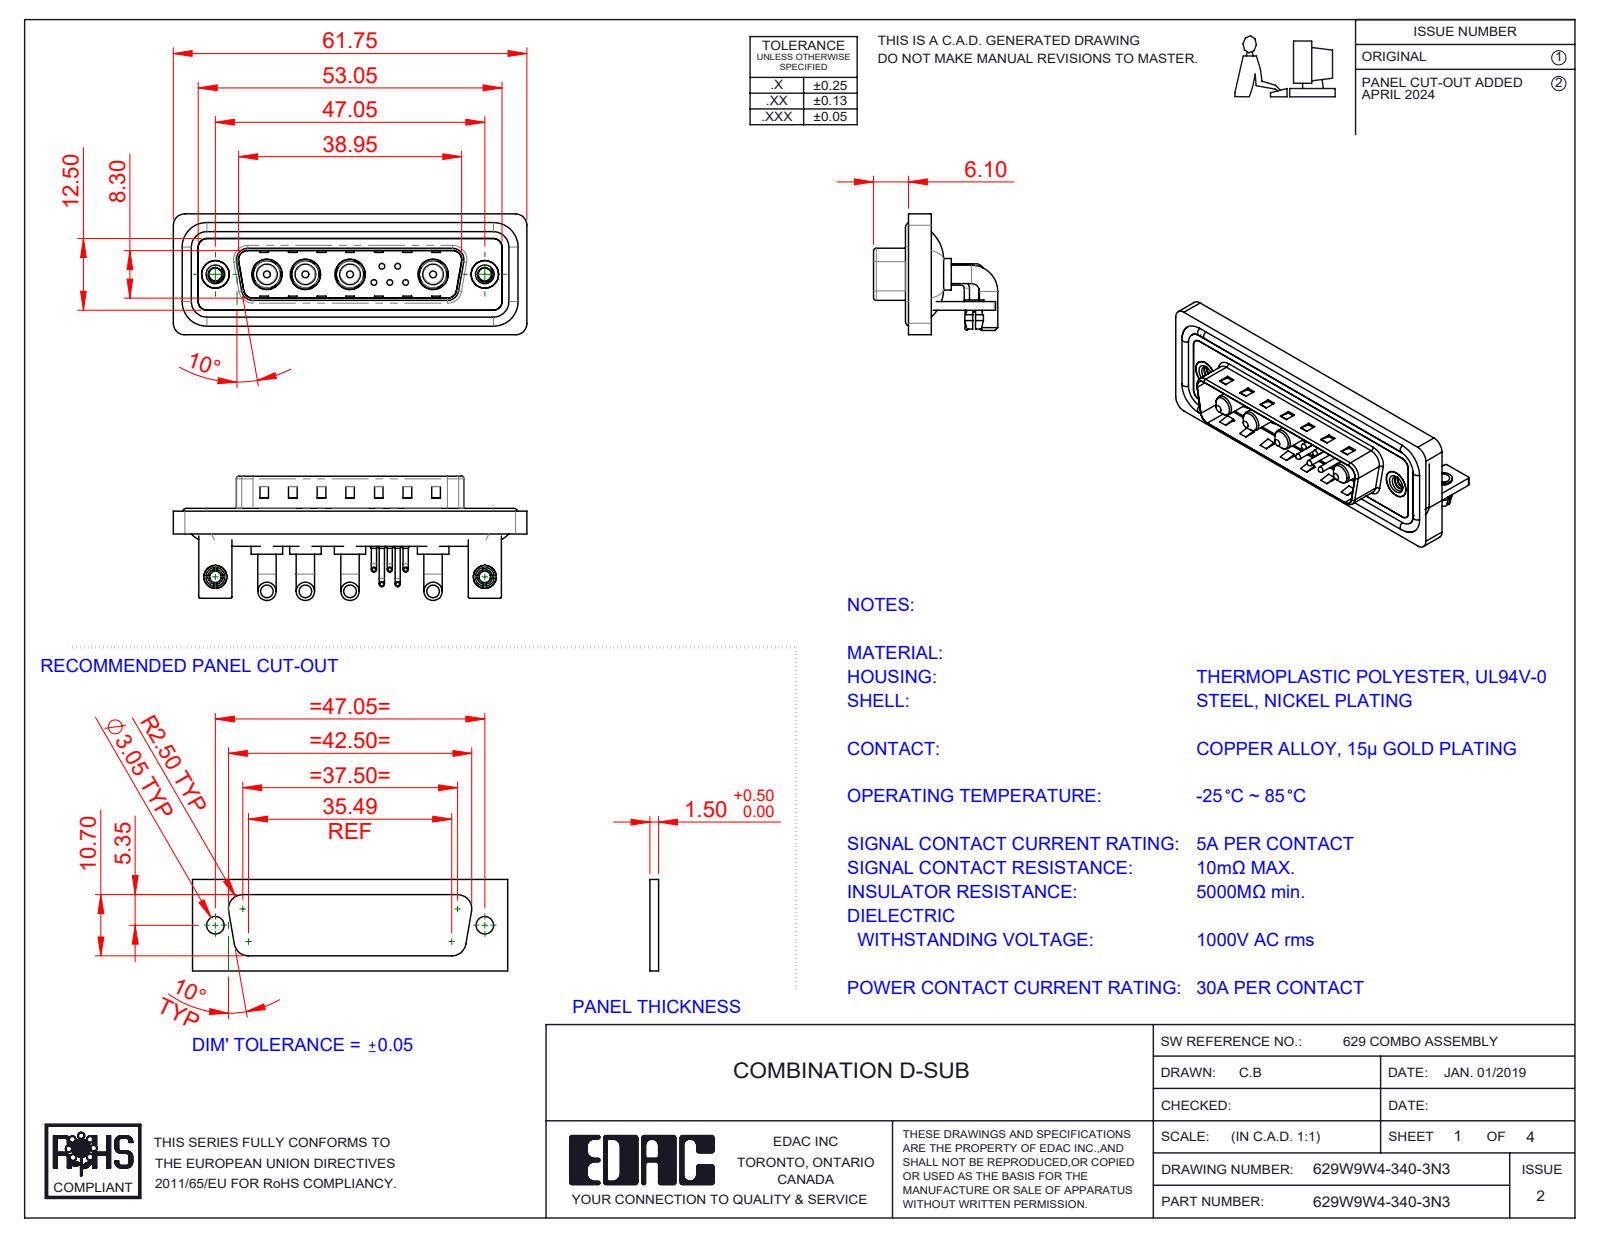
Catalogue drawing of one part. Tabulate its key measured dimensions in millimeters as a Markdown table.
| quantity | value |
| --- | --- |
| part name | 629Combo Contact Row 1; 629Combo Stabilizer Bracket; Power Pin_30A RA; 629Combo Waterproof Housing_25 Contacts (+7 more) |
| STEP written by | SolidWorks 2023 (CONFIG_CONTROL_DESIGN) |
| units | millimeters |
| bodies | 24 solids, 1337 faces (637 planar, 502 cylindrical, 198 other) |
| overall size | 61.75 × 21.7 × 21.1 |
| volume | 8 130 mm³ |
| surface area | 13 248 mm² |
| round holes (diameter × count) | 2 × 7, 0.75 × 5, 1.6 × 5, 4.85 × 4, 5.3 × 4, 2.26 × 2, 2.5 × 2, 3.2 × 2, 4 × 2, 4.8 × 2, 5 × 2 |
| round bosses / shafts (diameter × count) | 0.9 × 10, 3.2 × 8, 1.5 × 5, 1 × 5, 0.65 × 5, 5.5 × 4, 5.2 × 4, 4.75 × 4 |
| partial cylindrical surfaces (radius × count) | 2 × 19, 1.5 × 18, 0.25 × 16, 0.5 × 9, 1.6 × 8, 1.01 × 5, 0.6 × 4, 0.65 × 4 |
| main face-to-face distances | 0.4, 1.5, 0.8, 2.9, 2.1, 1.1, 3.7, 4.1, 4.5, 1.6 |
| hole center spacings | 3.16, 2.77, 5.04, 14.5, 47.05, 2.78, 4.4, 4.41 |
